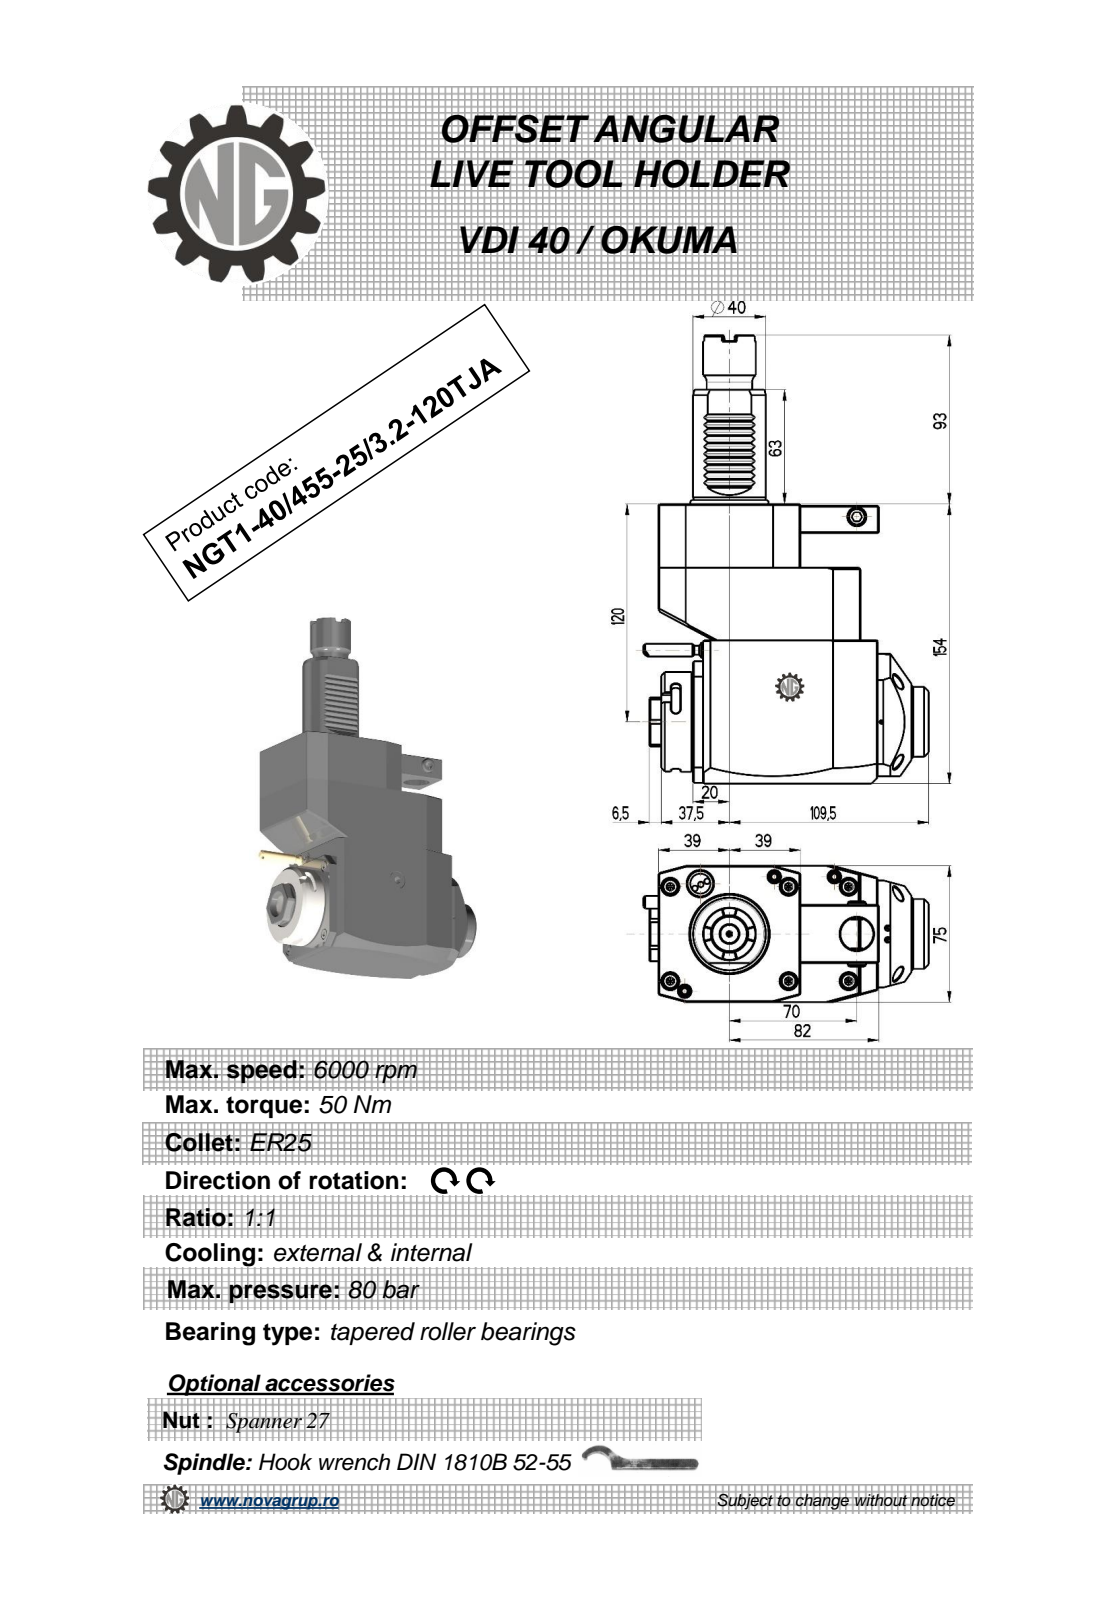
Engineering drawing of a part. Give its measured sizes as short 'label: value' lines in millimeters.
name: NGT1_40_455_25_3_2_120TJA
written by: PRO/ENGINEER BY PARAMETRIC TECHNOLOGY CORPORATION, 2010280 (CONFIG_CONTROL_DESIGN)
unit: mm
bodies: 1 solid, 381 faces (199 planar, 74 cylindrical, 108 other)
size: 247 × 156.83 × 75
volume: 1 302 000 mm³; area: 93 451 mm²
holes: 2× ⌀18, 1× ⌀2.5, 1× ⌀3, 1× ⌀9.5
bosses: 2× ⌀8.96, 1× ⌀55, 1× ⌀48, 1× ⌀40, 1× ⌀38.5, 1× ⌀29, 1× ⌀25, 1× ⌀10
rounds: 10× R0.3, 6× R2.5, 2× R180, 1× R0.5, 1× R4.25, 1× R10, 1× R15, 1× R24.5
face distances: 75, 154, 19, 119, 59, 111, 92, 35, 17.5, 53.5
hole spacings: 43.2, 75.07, 112.5
